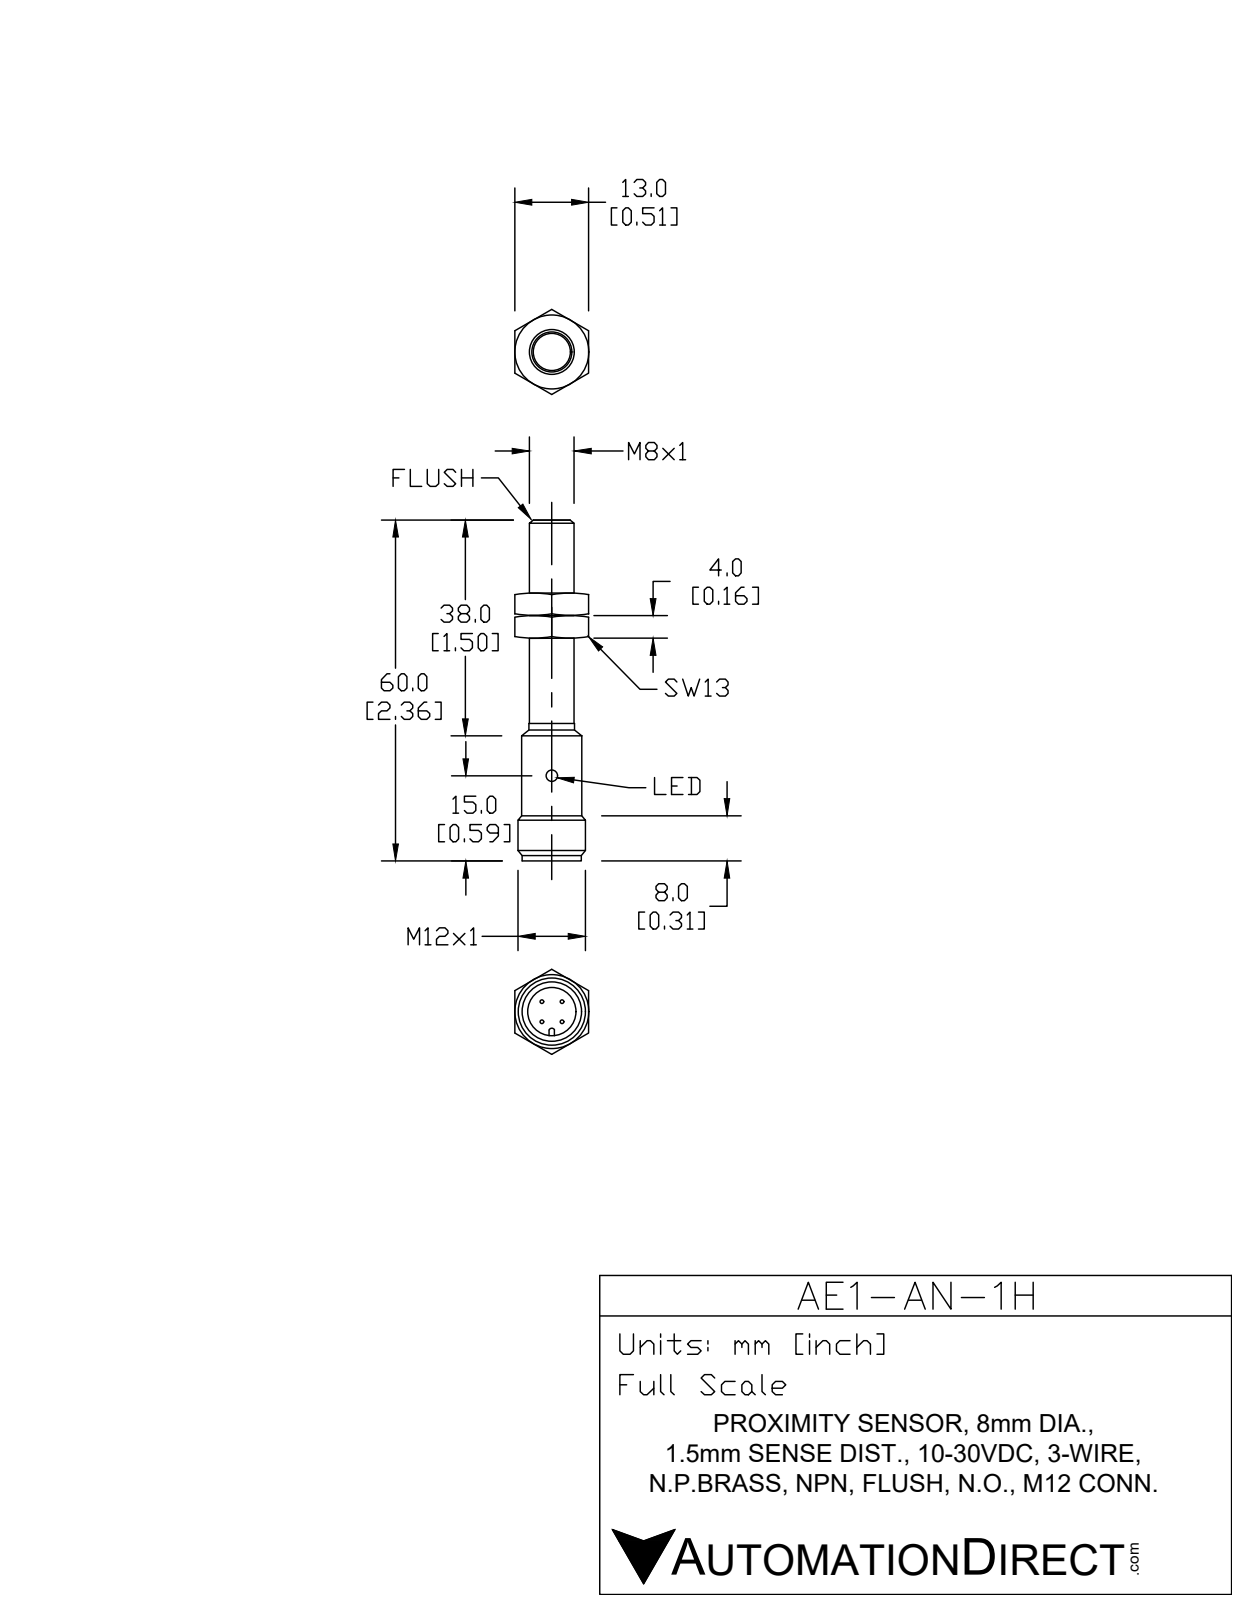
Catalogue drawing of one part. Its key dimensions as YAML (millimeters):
part_name: "AE1-AN-1H"
step_written_by: "SolidWorks 2017 (AUTOMOTIVE_DESIGN)"
units: millimeters
bodies: {solids: 7, faces: 137, planar: 33, cylindrical: 74, other: 30}
overall_size: [59.9, 12, 12]
volume: 3360
surface_area: 3236
round_holes:
  - {diameter: 1, count: 4}
  - {diameter: 2, count: 2}
  - {diameter: 6.2, count: 1}
  - {diameter: 8.4, count: 1}
  - {diameter: 9.9, count: 1}
round_bosses_or_shafts:
  - {diameter: 1.1, count: 4}
  - {diameter: 12, count: 1}
  - {diameter: 10.5, count: 1}
  - {diameter: 9.7, count: 1}
  - {diameter: 9.6, count: 1}
  - {diameter: 8, count: 1}
  - {diameter: 6.5, count: 1}
  - {diameter: 1, count: 1}
partial_cylinders:
  - {radius: 1.3, count: 4}
  - {radius: 0.6, count: 1}
  - {radius: 1.3, count: 1}
  - {radius: 3.4, count: 1}
face_to_face_distances: [0.4, 8.9, 48.8, 49.2, 48.5, 48.9, 4.5, 4.2, 44.3, 44.7]
hole_center_spacings: [2.5, 3.5, 5]
